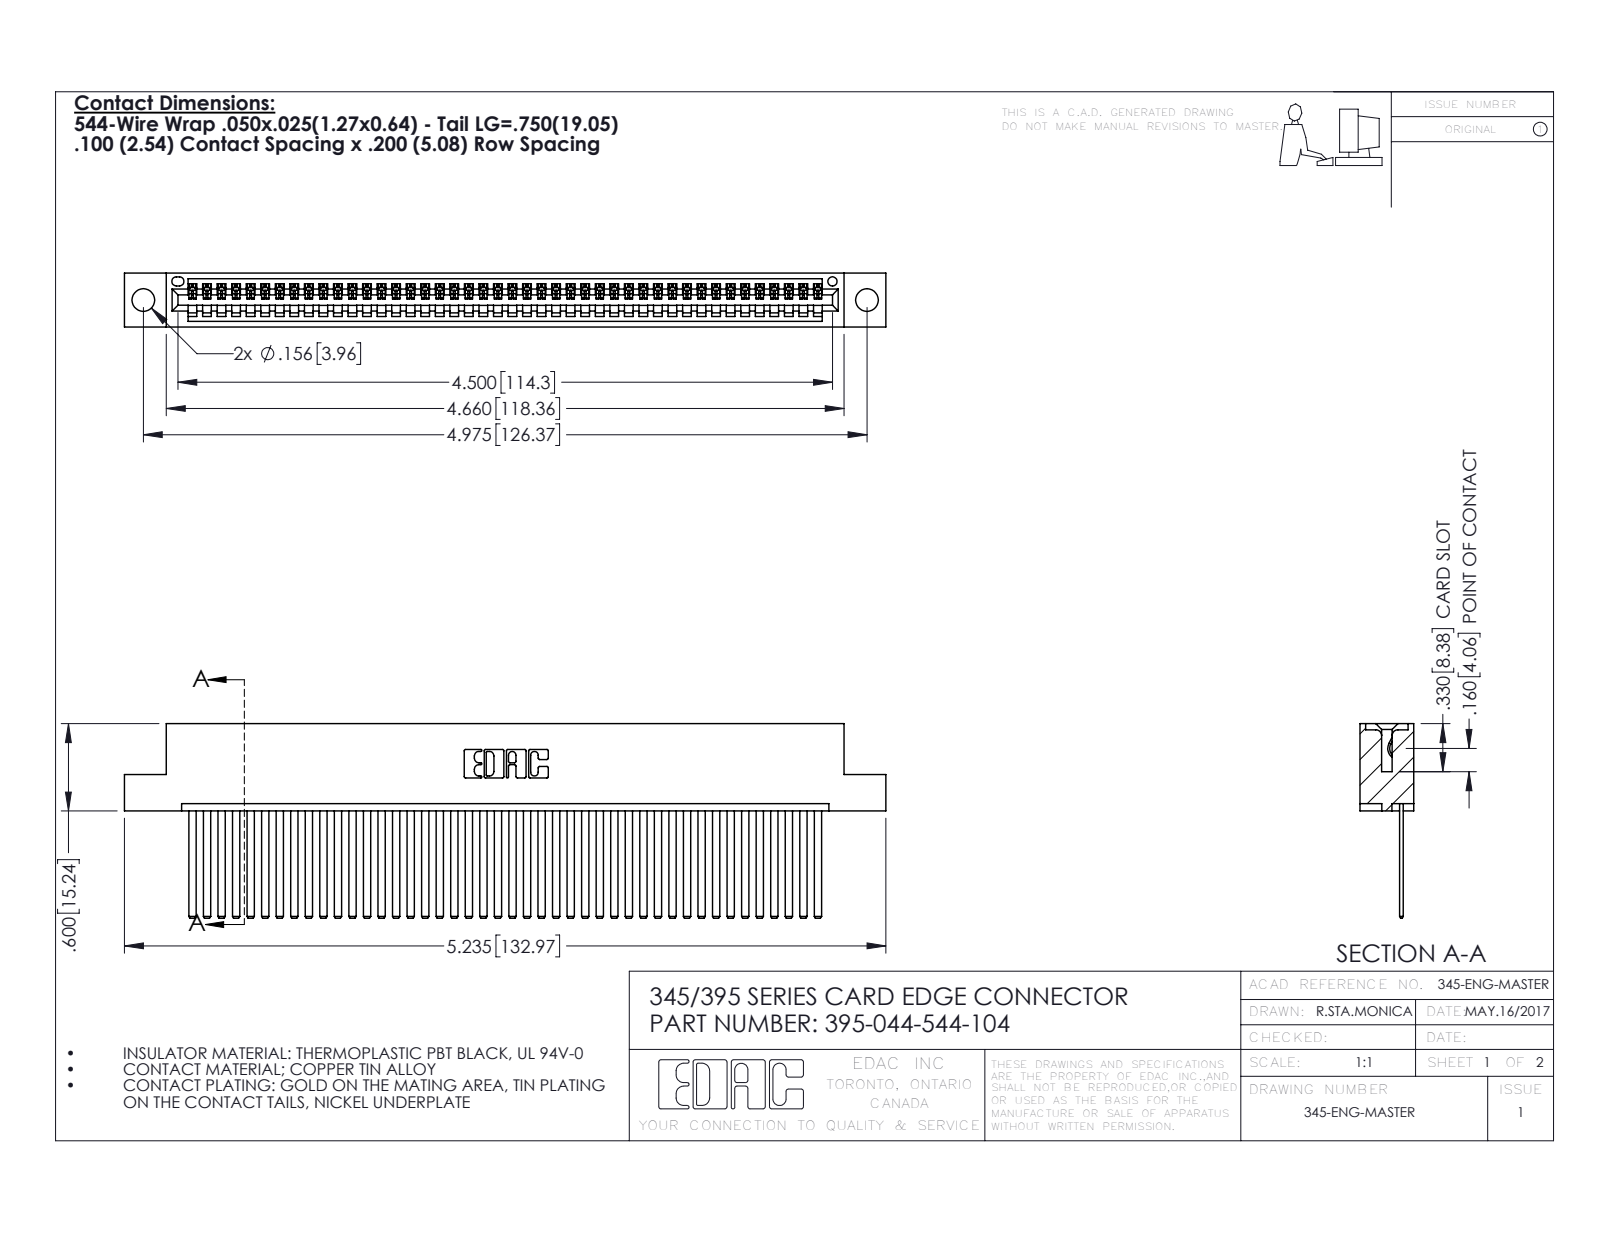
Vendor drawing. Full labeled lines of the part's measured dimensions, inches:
Part name (STEP PRODUCT): 395-044-544-104; 345-292-001_345-293-144; 345 Part_Flush Mounting Lugs - 0.156 Dia-TH
STEP written by: SolidWorks 2016 (CONFIG_CONTROL_DESIGN)
Units: inches
Bodies: 45 solids, 2414 faces (1664 planar, 750 cylindrical, 0 other)
Overall size (bounding box): 5.235 × 1.337 × 0.37
Volume: 0.797 in³ · Surface area: 29.03 in²
Round holes (diameter × count): ⌀0.156 ×2, ⌀0.064 ×1
Partial cylindrical surfaces — rounded edges, fillets, slot ends (radius × count): R0.006 ×88, R0.01 ×22, R0.007 ×6, R0.031 ×6, R0.026 ×3, R0.031 ×2, R0.04 ×2, R0.014 ×1
Main face-to-face distances: 0.072, 0.298, 0.025, 0.098, 0.272, 0.37, 0.2, 0.225, 0.149, 0.072
Hole centre spacings: 0.27, 4.739, 4.975
